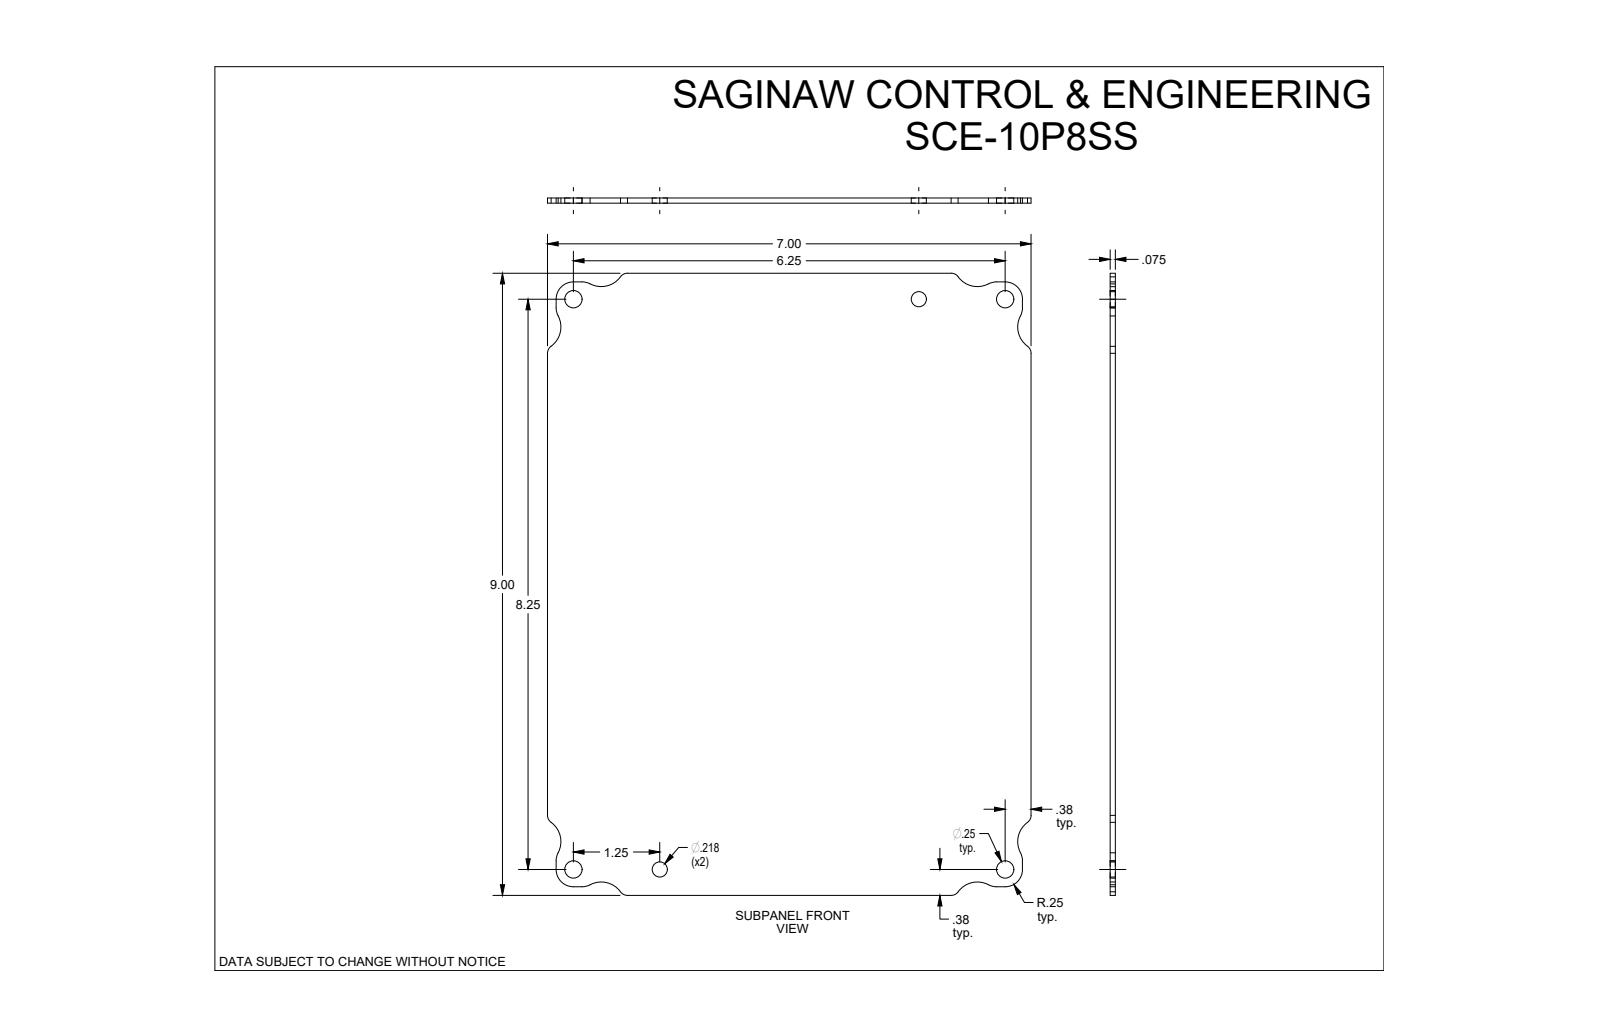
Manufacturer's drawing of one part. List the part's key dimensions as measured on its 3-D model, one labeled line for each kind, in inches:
Part name (STEP PRODUCT): SCE-10P8SS
STEP written by: SolidWorks 2019 (CONFIG_CONTROL_DESIGN)
Units: inches
Bodies: 1 solid, 48 faces (14 planar, 34 cylindrical, 0 other)
Overall size (bounding box): 9 × 7 × 0.075
Volume: 4.615 in³ · Surface area: 125.7 in²
Round holes (diameter × count): ⌀0.25 ×4, ⌀0.218 ×2
Partial cylindrical surfaces — rounded edges, fillets, slot ends (radius × count): R0.25 ×12, R0.125 ×8, R0.344 ×8
Main face-to-face distances: 0.075, 7, 9, 0.125, 8.875, 6.875, 8.75, 6.75
Hole centre spacings: 1.25, 5, 6.25, 8.25, 8.344, 9.646, 10.35, 9.062
